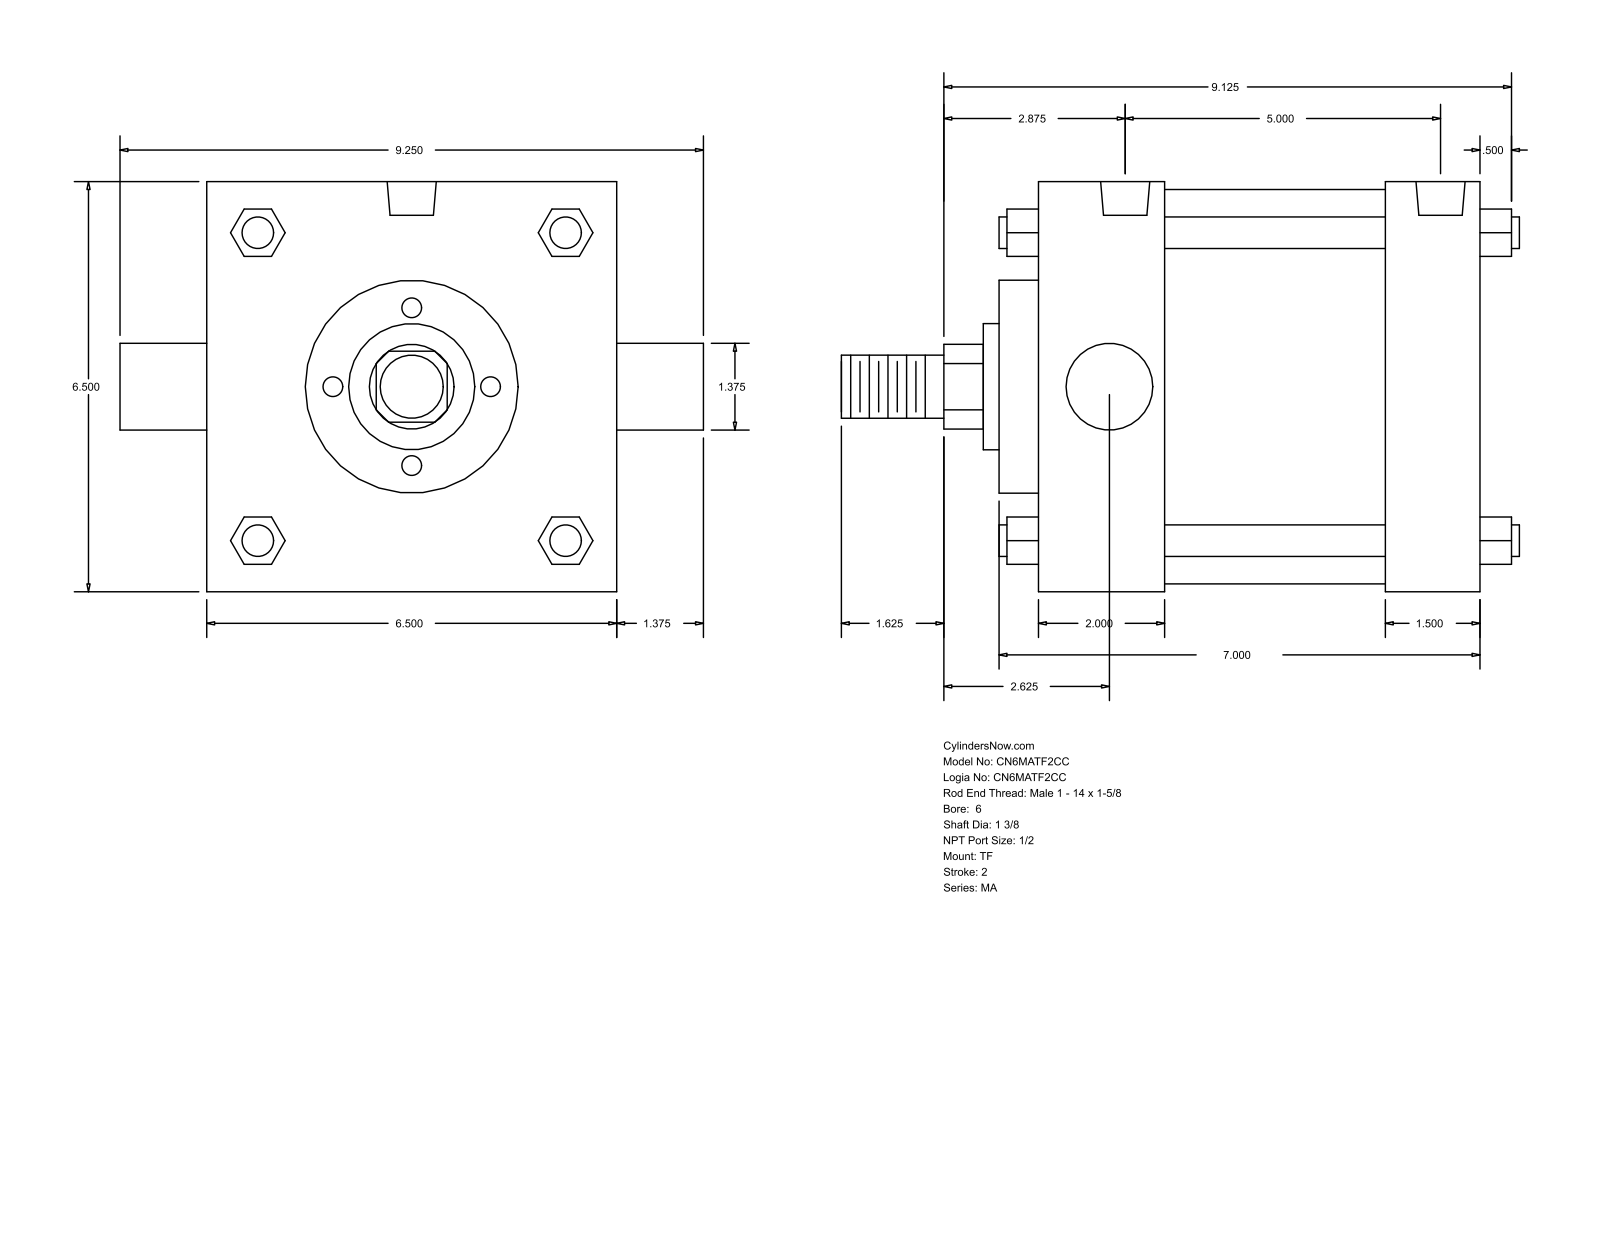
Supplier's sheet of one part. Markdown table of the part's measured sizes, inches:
| quantity | value |
| --- | --- |
| part name | MA_TF__0600_1.375 |
| STEP written by | GSSL Pune (CONFIG_CONTROL_DESIGN) |
| units | inches |
| bodies | 0 solids, 122 faces (93 planar, 29 cylindrical, 0 other) |
| overall size | 10.75 × 9.25 × 6.5 |
| round holes (diameter × count) | 0.687 × 3, 0.778 × 2 |
| round bosses / shafts (diameter × count) | 0.5 × 4, 1.375 × 2, 6.25 × 1, 3.375 × 1, 2 × 1, 1 × 1 |
| partial cylindrical surfaces (radius × count) | 0.672 × 1 |
| main face-to-face distances | 6.5, 7.125, 5.125, 1.5, 2, 5.625, 3.625, 2.625, 0.625, 6.25 |
| hole center spacings | 0.125, 5, 5.125 |
